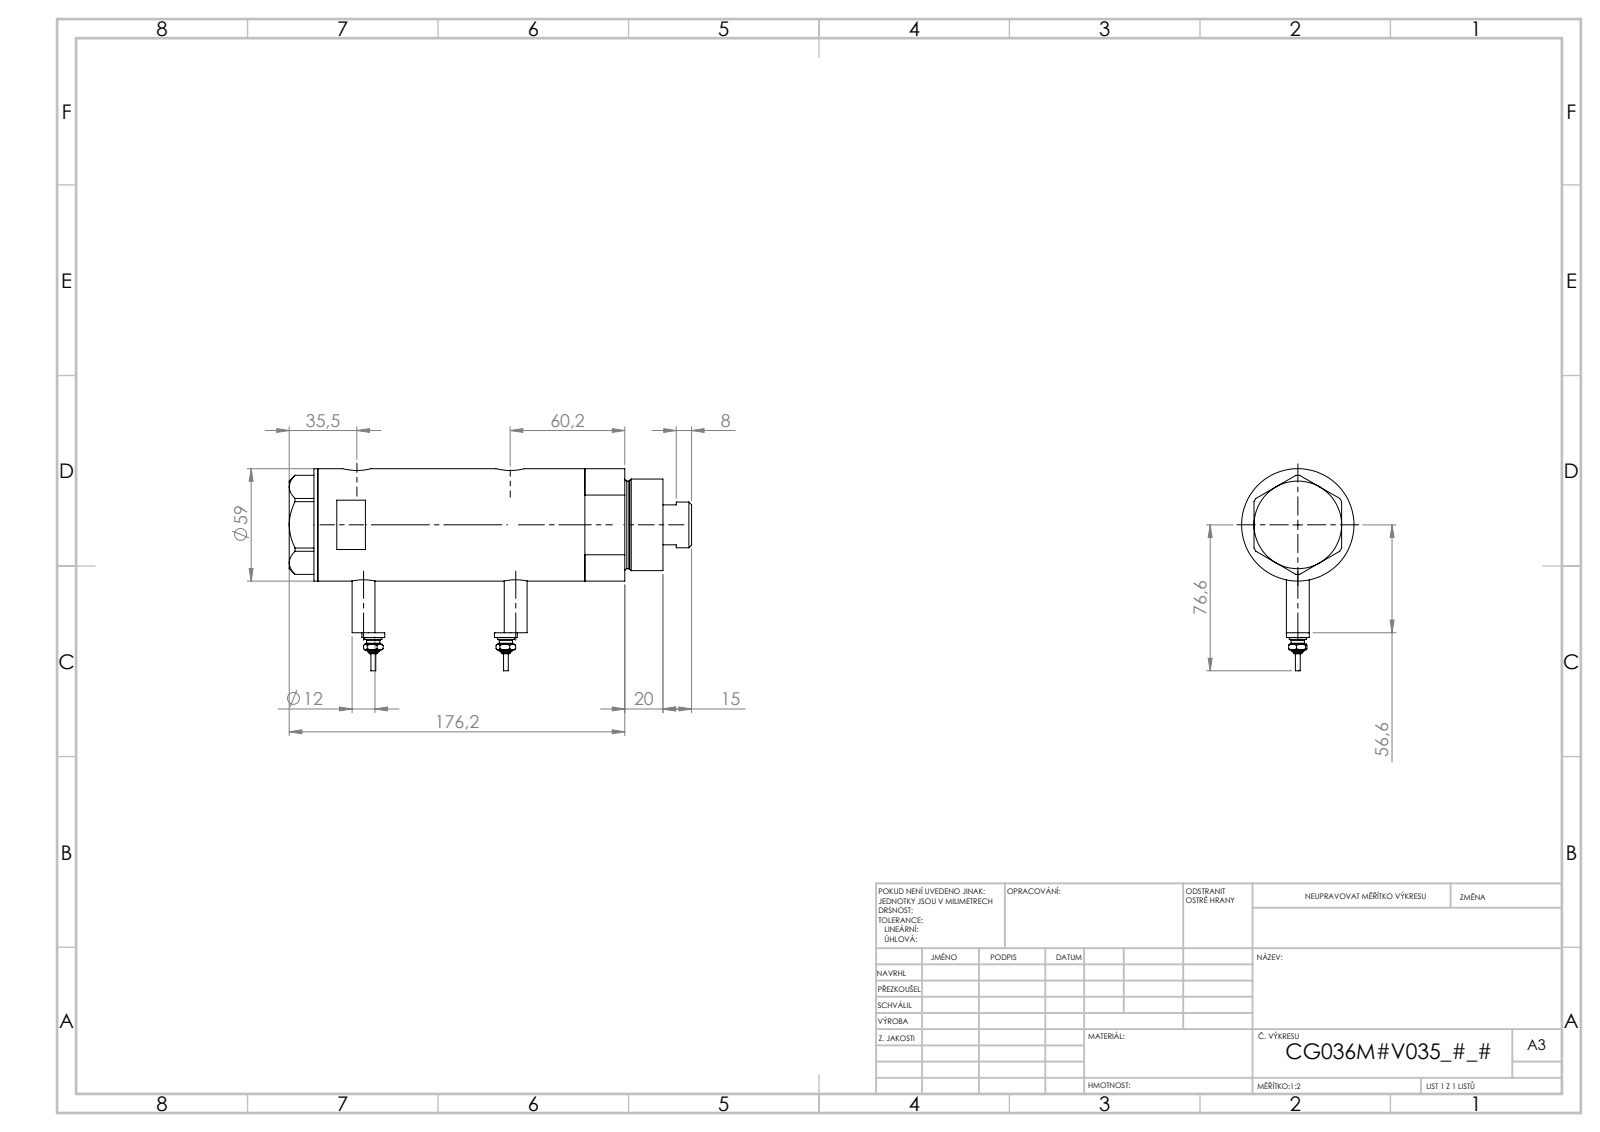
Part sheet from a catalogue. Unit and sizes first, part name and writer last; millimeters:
Units: millimetres
Overall size (bounding box): 198.42 × 91.3 × 59
Round holes (diameter × count): ⌀5 ×2, ⌀9.73 ×2, ⌀12.5 ×2, ⌀15 ×2, ⌀8.5 ×1, ⌀25 ×1, ⌀26.5 ×1, ⌀36 ×1, ⌀40 ×1, ⌀52 ×1
Round bosses / shafts (diameter × count): ⌀12 ×3, ⌀9 ×2, ⌀7 ×2, ⌀4.34 ×2, ⌀2.4 ×2, ⌀59 ×1, ⌀48 ×1, ⌀46 ×1
Main face-to-face distances: 92.34, 23.5, 68.84, 15, 38.5, 107.34, 183.42, 168.42, 144.92, 76.08
Hole centre spacings: 2.9, 3.5, 67.15, 70.05, 70.65, 73.55, 2.89, 2.91
Volume: 451 242 mm³ · Surface area: 97 034 mm²
Bodies: 6 solids, 232 faces (81 planar, 77 cylindrical, 74 other)
Part name (STEP PRODUCT): V270CG_SWITCH; V270CG_MIDDLE; V270CG_BACK; V270CG_FRONT (+1 more)
STEP written by: SolidWorks 2019 (CONFIG_CONTROL_DESIGN)
